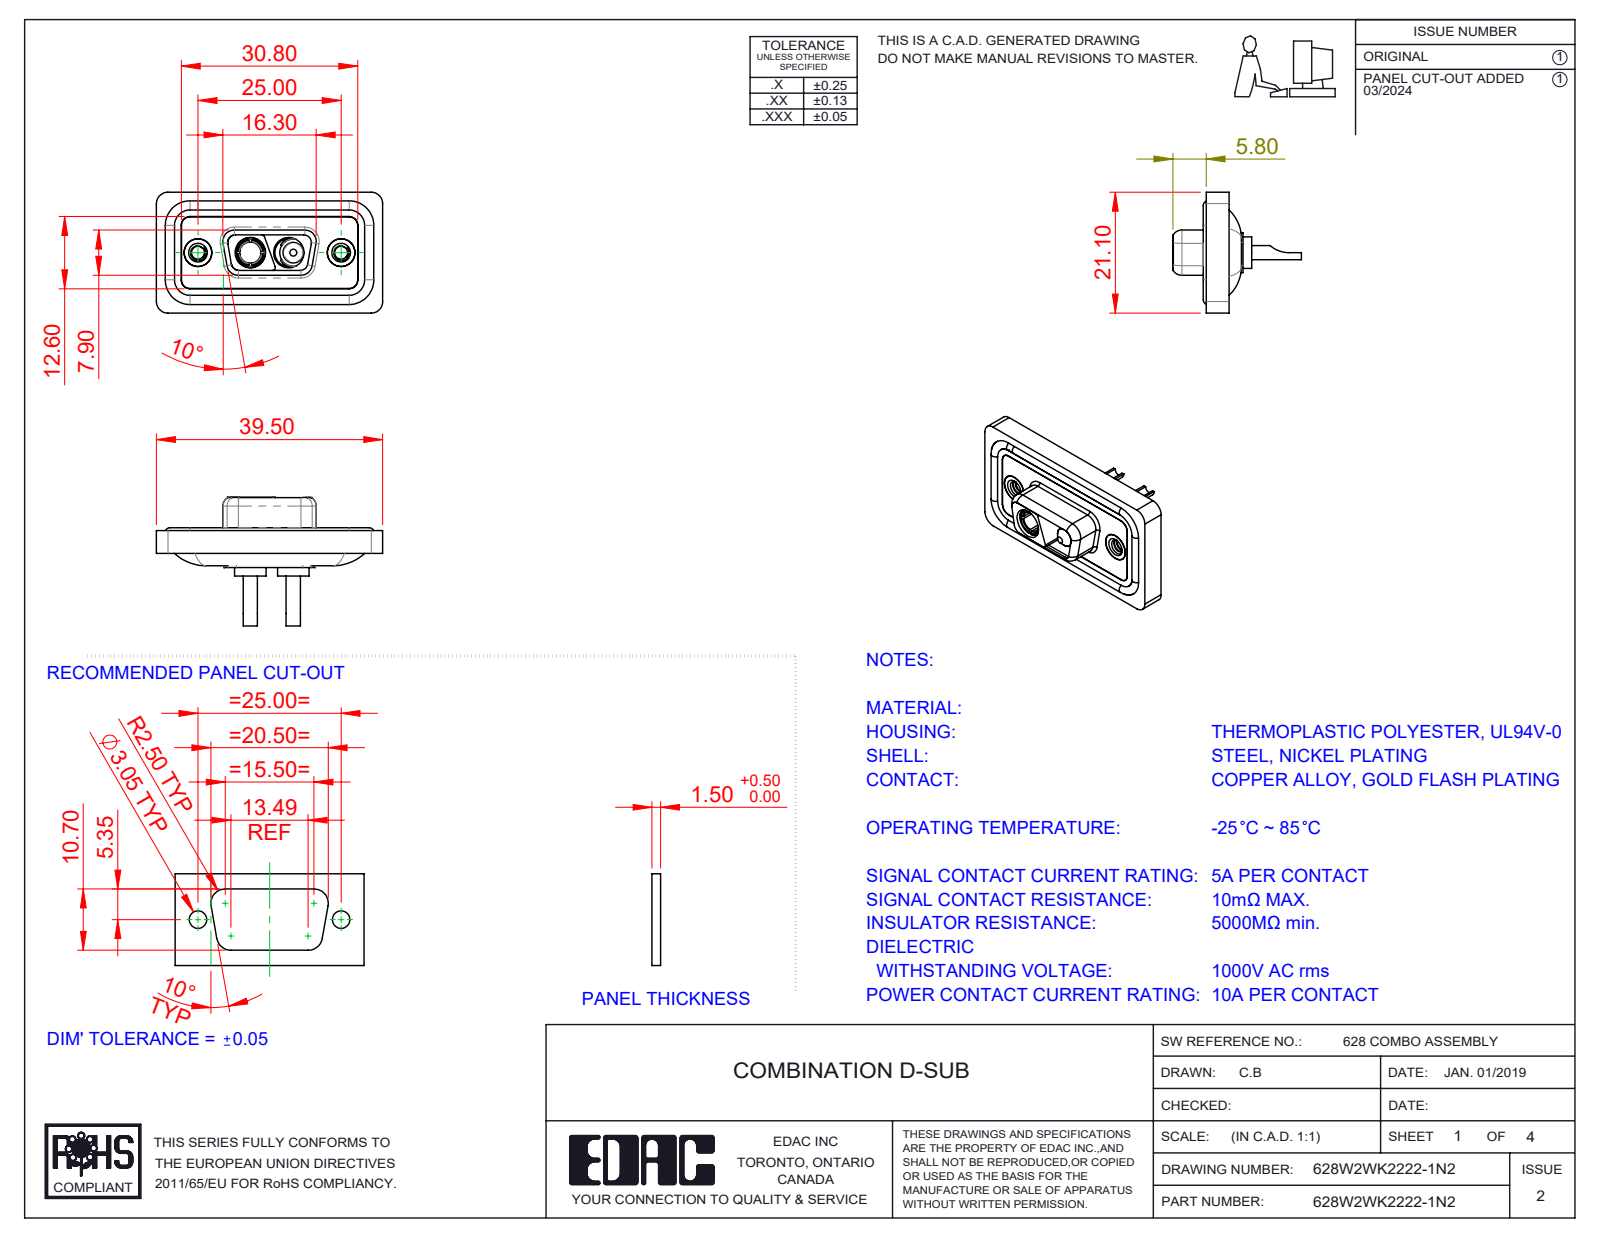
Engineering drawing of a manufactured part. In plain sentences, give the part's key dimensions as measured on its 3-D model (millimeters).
The part is named "628Combo Housing_2WK2; Power Socket_10A SC; 628Combo Waterproof Housing_09 Contacts; 628Combo Threaded Rivet_2 (+4 more)". Its 3-D file was written by "SolidWorks 2023 (CONFIG_CONTROL_DESIGN)". It is 11 solids with 510 faces: 148 planar, 237 cylindrical and 125 other. Overall it measures 39.5 by 22.45 by 21.1 millimeters. Its volume is 4 597 cubic millimeters and its surface area 7 439 square millimeters. Round holes: 4 of diameter 4.85, 2 of diameter 1.7, 2 of diameter 2.26, 2 of diameter 4, 2 of diameter 4.05, 2 of diameter 5, 2 of diameter 5.3, 1 of diameter 3.7. Round bosses or shafts: 4 of diameter 1.6, 2 of diameter 5.5, 2 of diameter 5.2, 2 of diameter 4.95, 2 of diameter 4.8, 2 of diameter 4.75, 2 of diameter 3.75, 2 of diameter 2.5. Partial cylindrical surfaces (rounded edges, fillets, slot ends): 22 of radius 1.5, 18 of radius 2, 8 of radius 1.35, 8 of radius 1.6, 6 of radius 0.5, 4 of radius 0.25, 4 of radius 0.6, 4 of radius 0.65. The main face-to-face distances are 0.4, 1.1, 2.9, 1.6, 0.5, 1.8, 5.65, 1.5, 5.35, 3.1. The hole center spacings are 9.14, 15.86, 6.72, 25.
